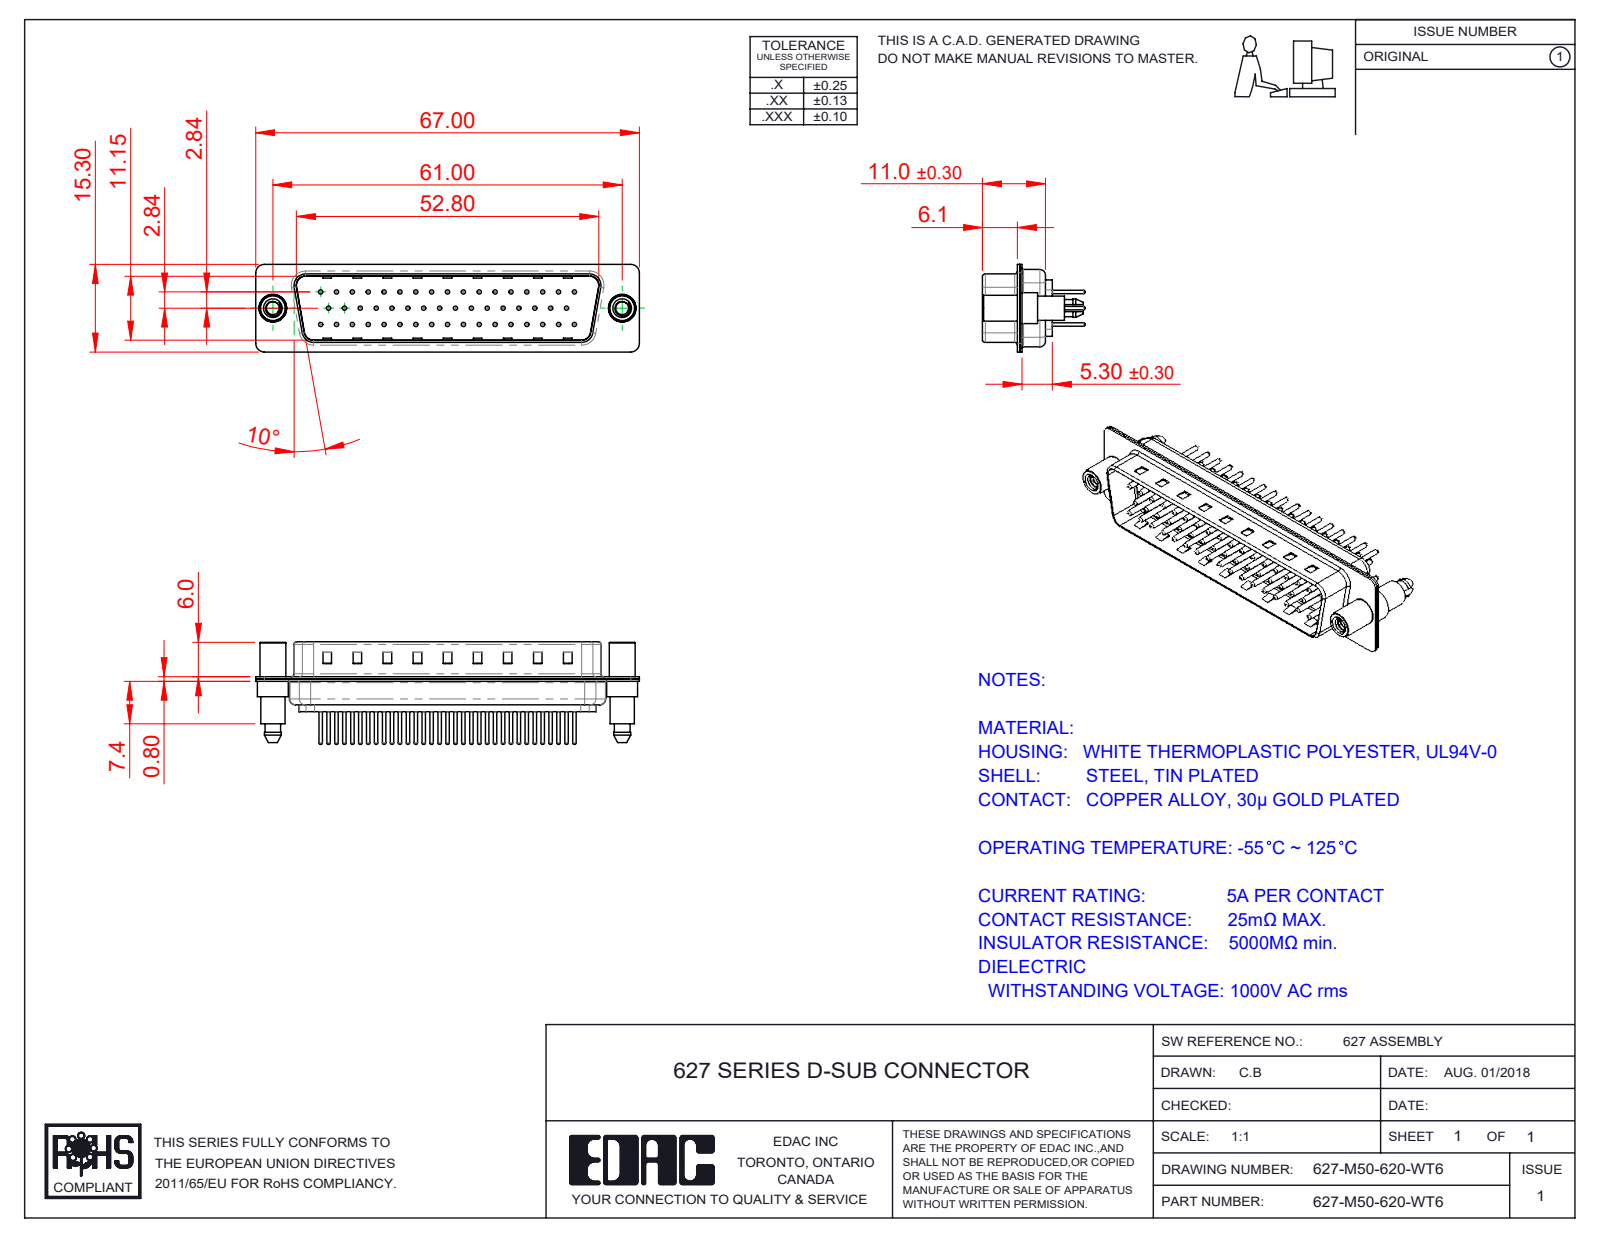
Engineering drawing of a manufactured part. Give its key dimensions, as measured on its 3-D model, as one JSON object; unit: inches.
{"part_name": "627M 4-40 Threaded Standoff and Boardlock; 627M Contact Row 3_20; 627M Housing_50 Contacts; 627-M50-620-WT6 (+4 more)", "step_written_by": "SolidWorks 2020 (CONFIG_CONTROL_DESIGN)", "units": "inches", "bodies": {"solids": 55, "faces": 2314, "planar": 571, "cylindrical": 869, "other": 874}, "overall_size": [2.638, 0.705, 0.602], "volume_in3": 0.297, "surface_area_in2": 17.31, "round_holes": [[0.03, 50], [0.063, 50], [0.079, 50], [0.089, 2], [0.157, 2], [0.189, 2]], "round_bosses_or_shafts": [[0.059, 50], [0.024, 50], [0.213, 2], [0.193, 2], [0.177, 2], [0.167, 2]], "partial_cylinders_radius": [[0.059, 18], [0.079, 12], [0.063, 10], [0.02, 8], [0.01, 4], [0.024, 4], [0.026, 4], [0.035, 4]], "face_to_face_distances": [0.016, 0.455, 0.224, 0.24, 0.031, 0.03, 0.485, 0.209, 0.485, 0.516], "hole_center_spacings": [0.124, 0.109, 0.218, 0.327, 0.436, 0.545, 0.654, 0.198]}
